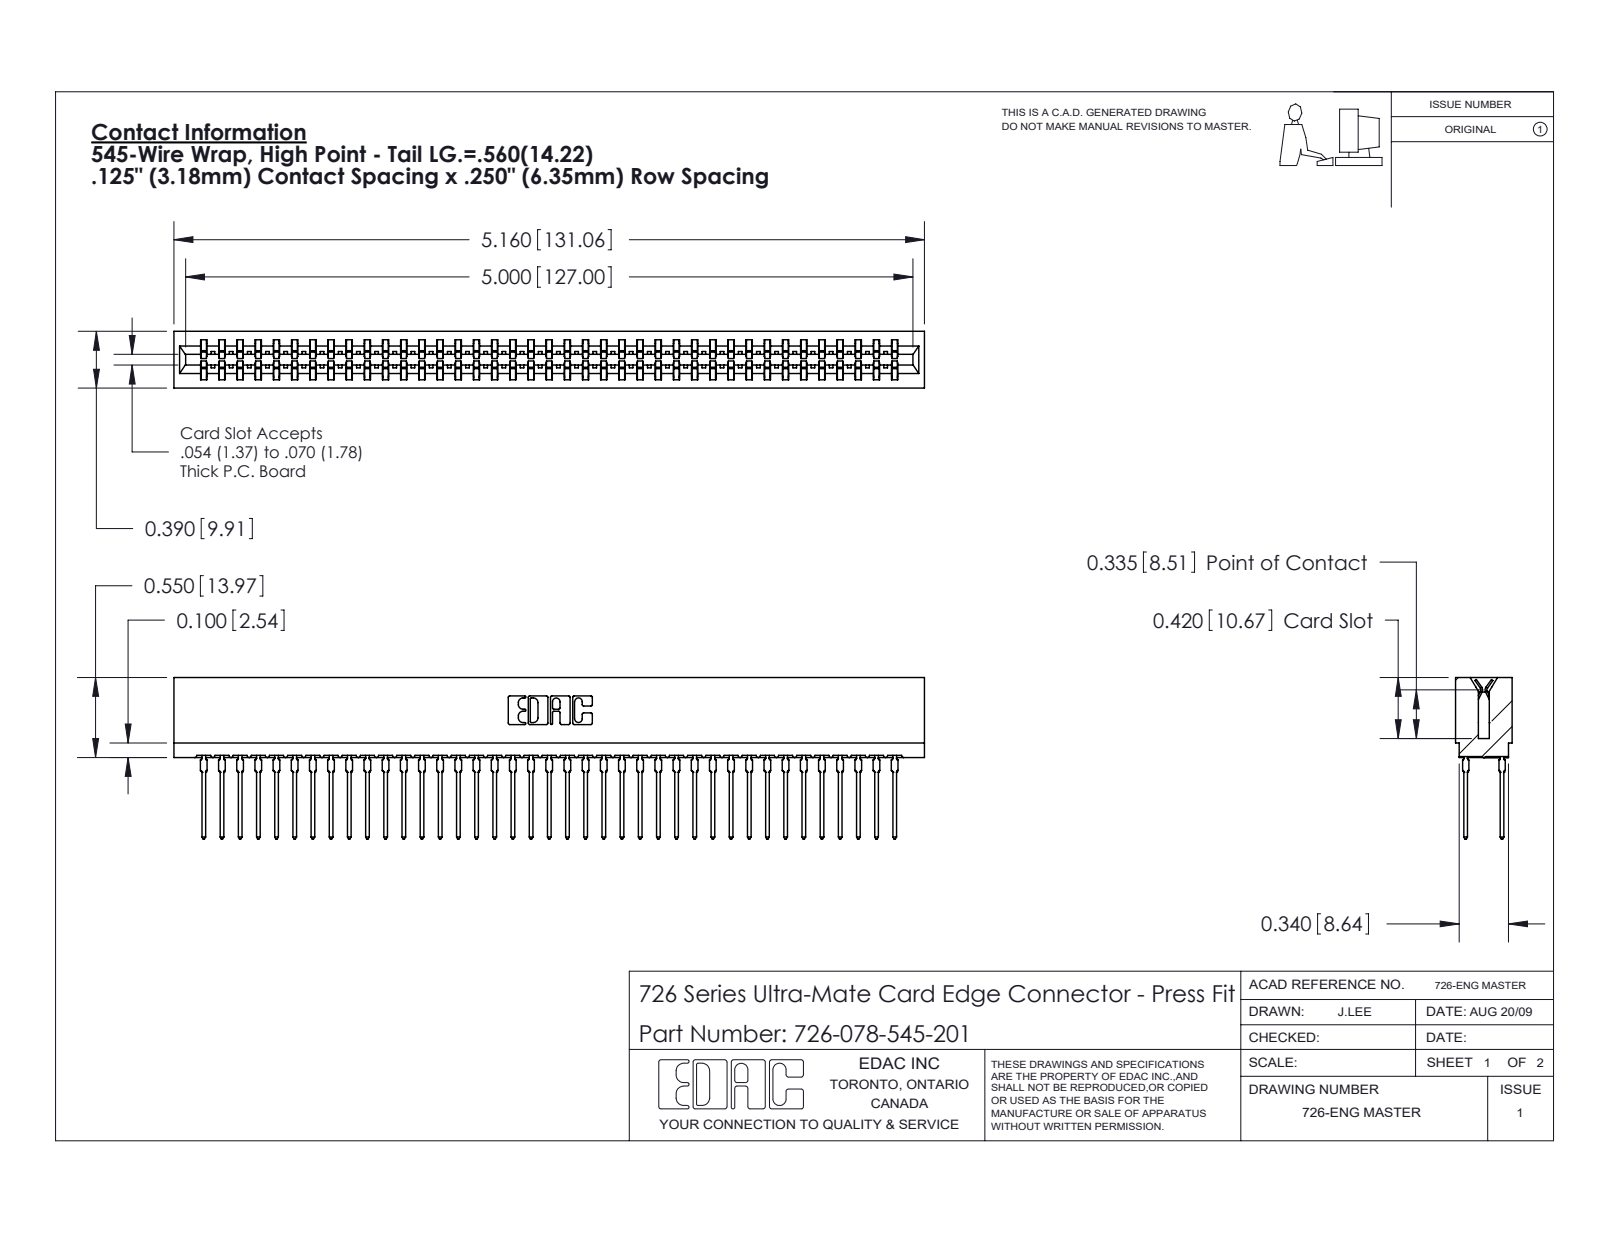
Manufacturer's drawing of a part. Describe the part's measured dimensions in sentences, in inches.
The part is named "746-292-001_545; 726-078-545-201; 726 Part_.515 Slot Depth - 01". Its 3-D file was written by "SolidWorks 2020 (CONFIG_CONTROL_DESIGN)". It is 79 solids with 7078 faces: 3643 planar, 1407 cylindrical and 2028 other. Overall it measures 5.16 by 1.109 by 0.39 inches. Its volume is 0.753 cubic inches and its surface area 33.74 square inches. Partial cylindrical surfaces (rounded edges, fillets, slot ends): 156 of radius 0.021, 40 of radius 0.015, 22 of radius 0.01, 8 of radius 0.005, 8 of radius 0.011, 6 of radius 0.007, 6 of radius 0.031, 3 of radius 0.026. The main face-to-face distances are 0.057, 0.333, 0.025, 0.307, 0.39, 0.25, 0.083, 0.275, 0.365, 0.032.
